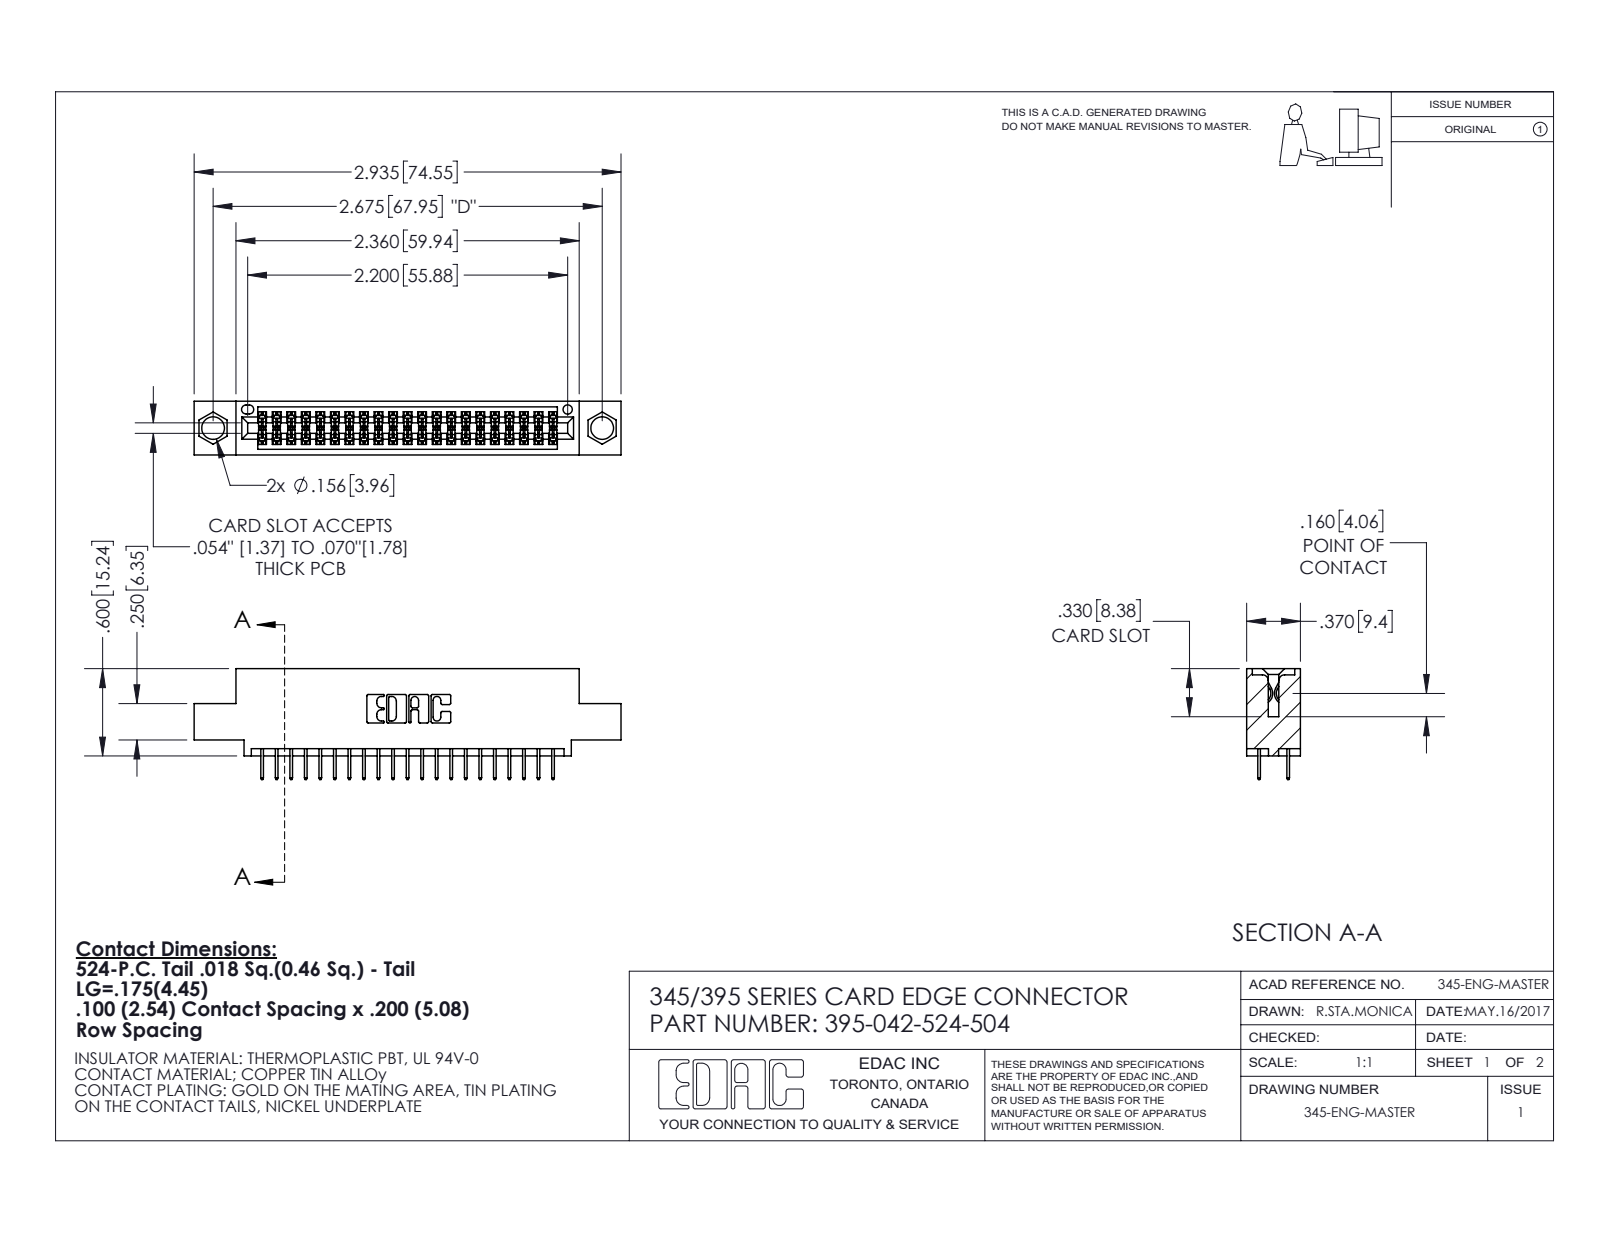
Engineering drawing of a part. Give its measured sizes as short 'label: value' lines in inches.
name: 345 Part_0.110 Offset - 0.156 Dia-TI; 345-292-001_345-293-124; 395-042-524-504
written by: SolidWorks 2020 (CONFIG_CONTROL_DESIGN)
unit: in
bodies: 43 solids, 2412 faces (1736 planar, 676 cylindrical, 0 other)
size: 2.935 × 0.762 × 0.37
volume: 0.415 in³; area: 14.61 in²
holes: 2× ⌀0.156, 1× ⌀0.064
rounds: 84× R0.006, 22× R0.01, 6× R0.007, 6× R0.031, 3× R0.026, 2× R0.014, 2× R0.019, 2× R0.022
face distances: 0.072, 0.298, 0.2, 0.37, 0.098, 0.272, 0.025, 0.225, 0.072, 0.175
hole spacings: 0.27, 2.441, 2.675
